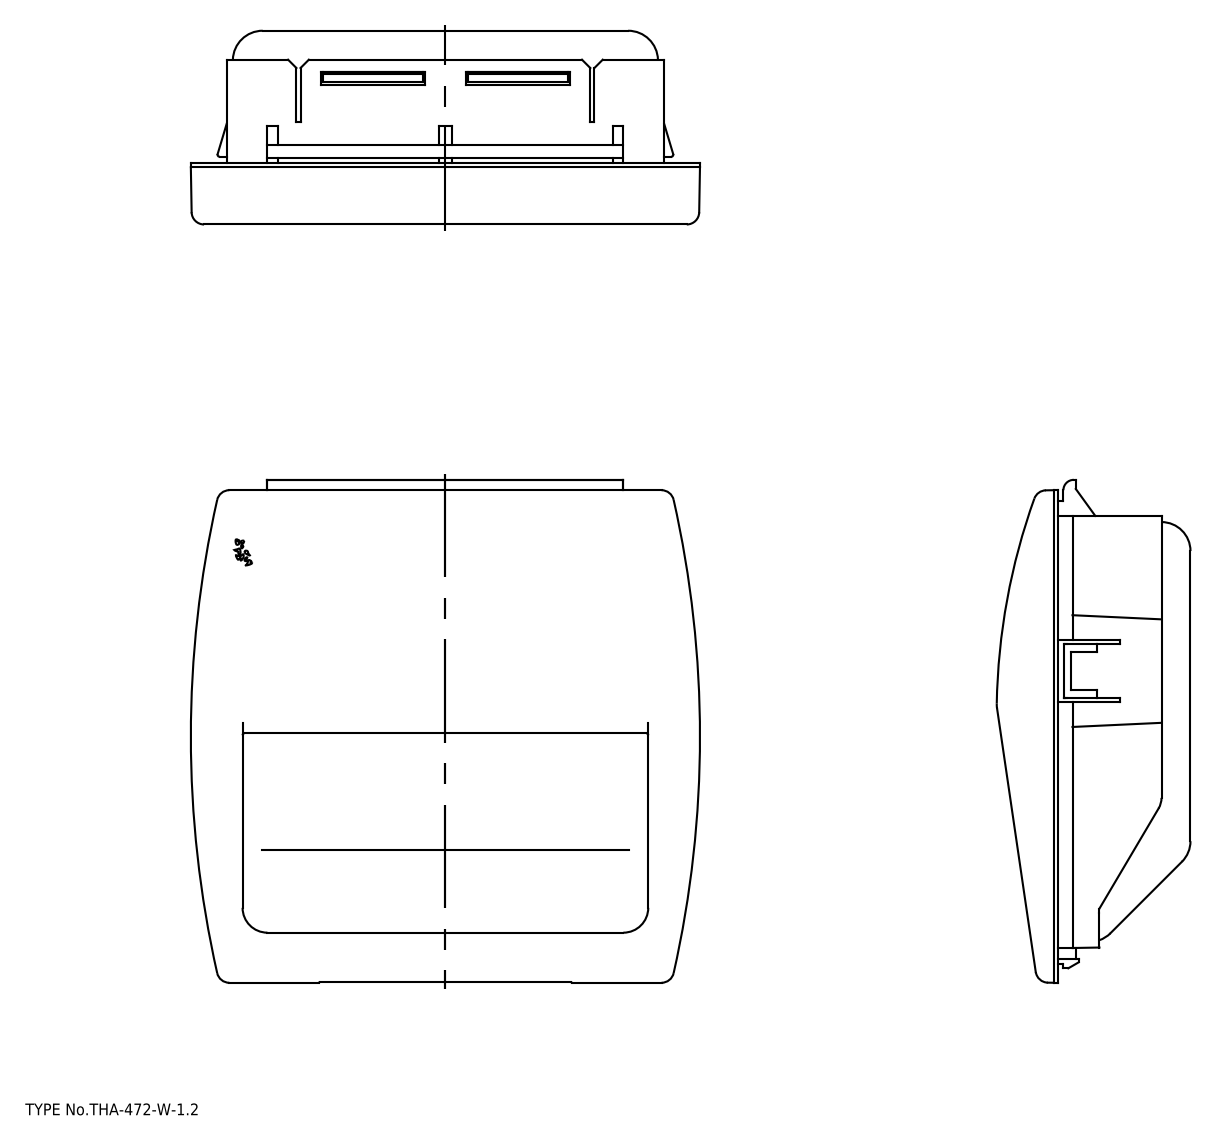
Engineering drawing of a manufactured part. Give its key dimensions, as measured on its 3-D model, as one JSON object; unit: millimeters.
{"part_name": "case; grip", "step_written_by": "spGate 19.8.4 (****-****-****-****) (AUTOMOTIVE_DESIGN)", "units": "millimeters", "bodies": {"solids": 3, "faces": 703, "planar": 273, "cylindrical": 266, "other": 164}, "overall_size": [123, 121.5, 46.8], "volume_mm3": 107561, "surface_area_mm2": 102425, "round_holes": [[3.4, 2]], "partial_cylinders_radius": [[0.5, 114], [1, 23], [7, 21], [5, 14], [0.3, 11], [8.5, 8], [0.6, 4], [3, 4]], "face_to_face_distances": [2, 104.2, 1.5, 3.5, 100.7, 102.7, 102.2, 32, 30, 98.7], "hole_center_spacings": [52]}
